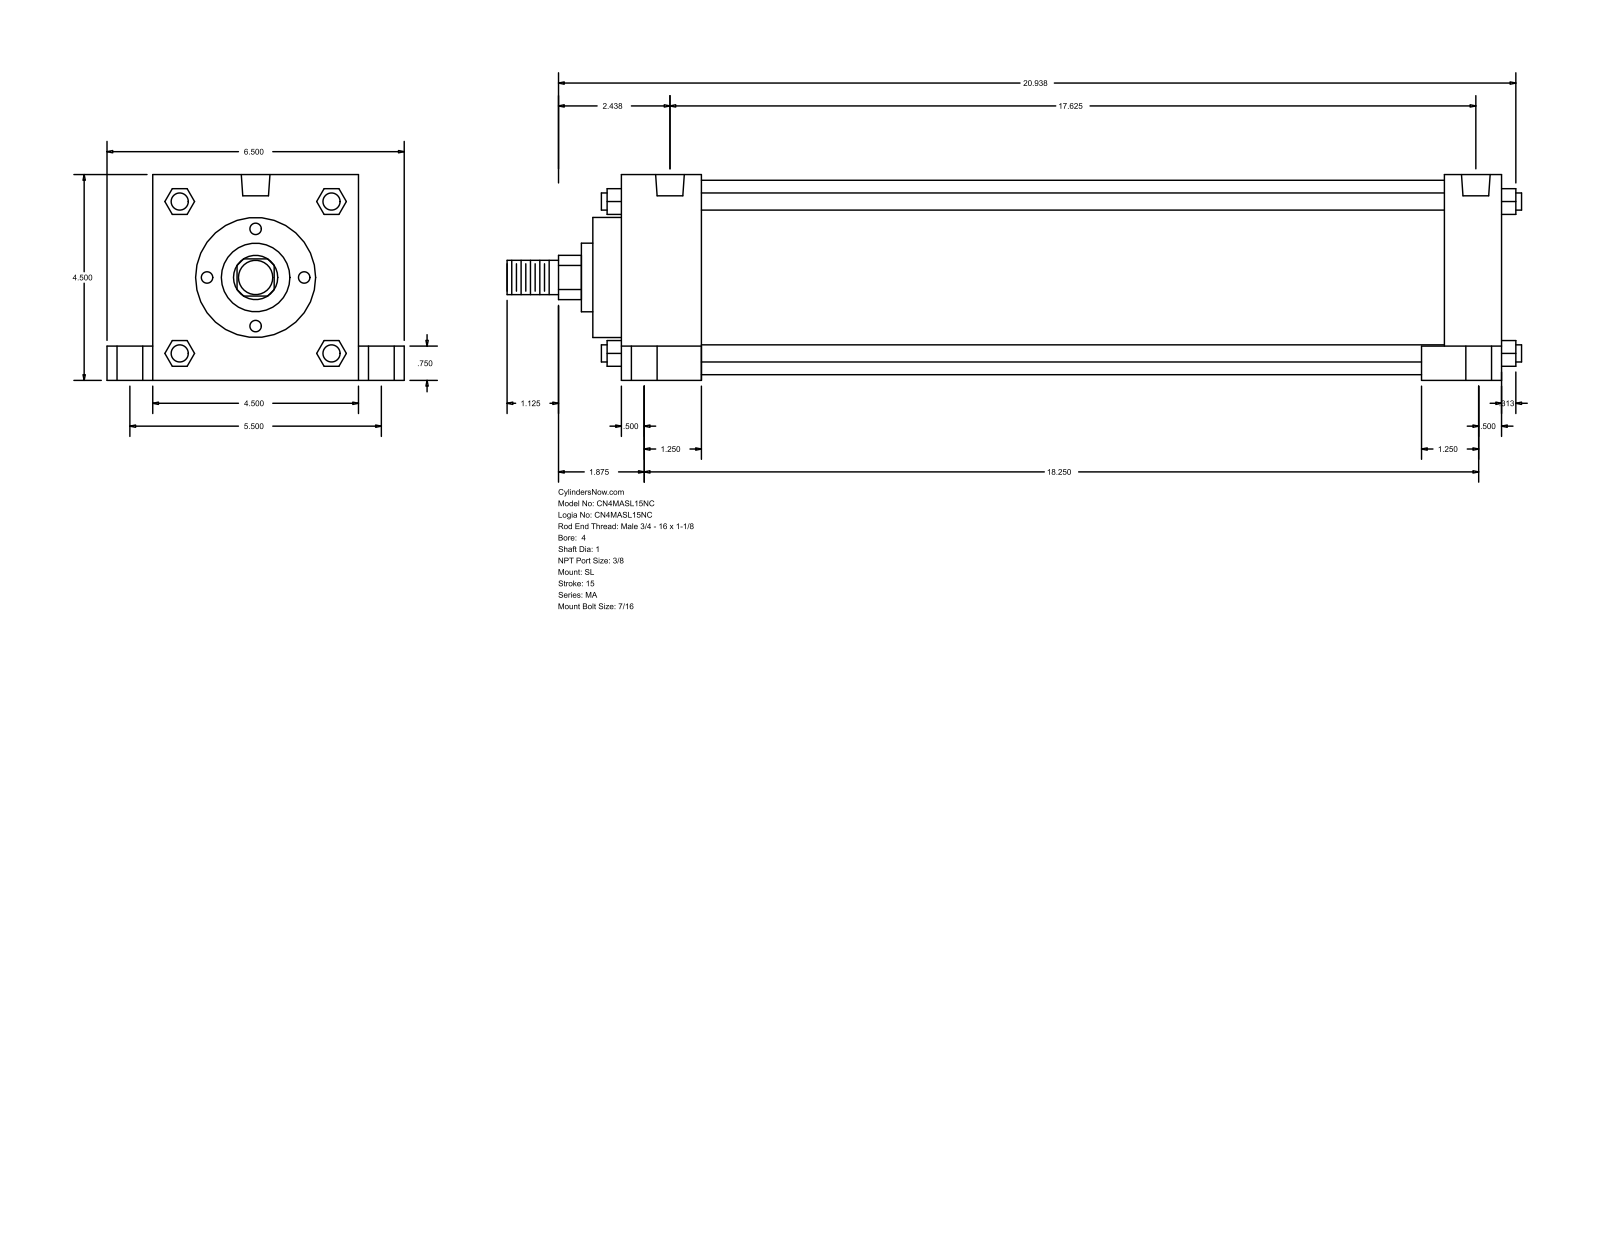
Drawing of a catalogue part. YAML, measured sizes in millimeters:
part_name: "MA_SL__0400_1"
step_written_by: "GSSL Pune (CONFIG_CONTROL_DESIGN)"
units: millimeters
bodies: {solids: 0, faces: 150, planar: 113, cylindrical: 37, other: 0}
overall_size: [563.56, 165.1, 114.3]
round_holes:
  - {diameter: 11.11, count: 4}
  - {diameter: 14.29, count: 4}
  - {diameter: 20.64, count: 4}
  - {diameter: 15.93, count: 2}
round_bosses_or_shafts:
  - {diameter: 9.53, count: 4}
  - {diameter: 107.95, count: 1}
  - {diameter: 66.67, count: 1}
  - {diameter: 38.1, count: 1}
  - {diameter: 25.4, count: 1}
  - {diameter: 19.05, count: 1}
partial_cylinders:
  - {radius: 12.29, count: 1}
face_to_face_distances: [114.3, 488.96, 44.46, 444.5, 457.2, 412.74, 31.76, 25.4, 139.7, 19.05]
hole_center_spacings: [69.87, 70.14, 71.3, 72.4, 139.7, 438.15, 449.96, 454.67]
